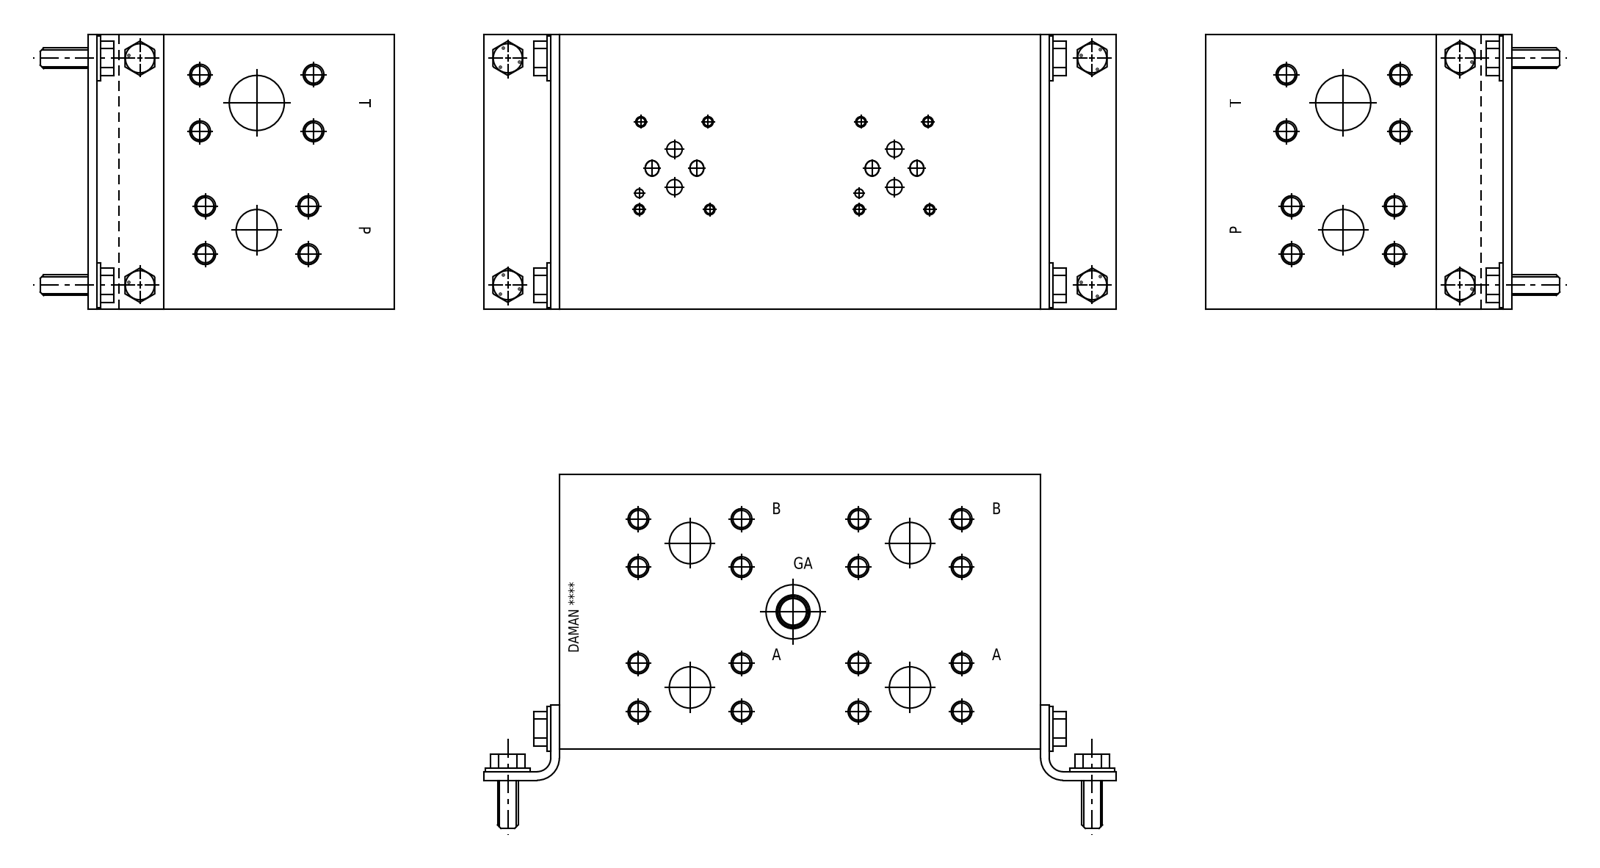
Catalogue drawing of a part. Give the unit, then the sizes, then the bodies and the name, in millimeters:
Units: millimetres
Overall size (bounding box): 222.25 × 127 × 127
Round holes (diameter × count): ⌀7.92 ×26, ⌀9.53 ×26, ⌀4.22 ×8, ⌀5 ×8, ⌀7.14 ×8, ⌀19.05 ×5, ⌀3.96 ×2, ⌀12.29 ×1, ⌀12.9 ×1, ⌀14.27 ×1, ⌀14.53 ×1, ⌀25.02 ×1
Main face-to-face distances: 127, 222.25, 22.1, 200.15, 104.9, 22.06, 21.31, 0.79, 126.21, 0.75
Hole centre spacings: 101.6, 26.26, 26.25, 47.59, 52.51, 60.46, 22.19, 66.68
Volume: 3 490 000 mm³ · Surface area: 180 302 mm²
Bodies: 1 solid, 708 faces (395 planar, 111 cylindrical, 202 other)
Part name (STEP PRODUCT): D03HP024F
STEP written by: Autodesk Inventor 2021 (AUTOMOTIVE_DESIGN)
